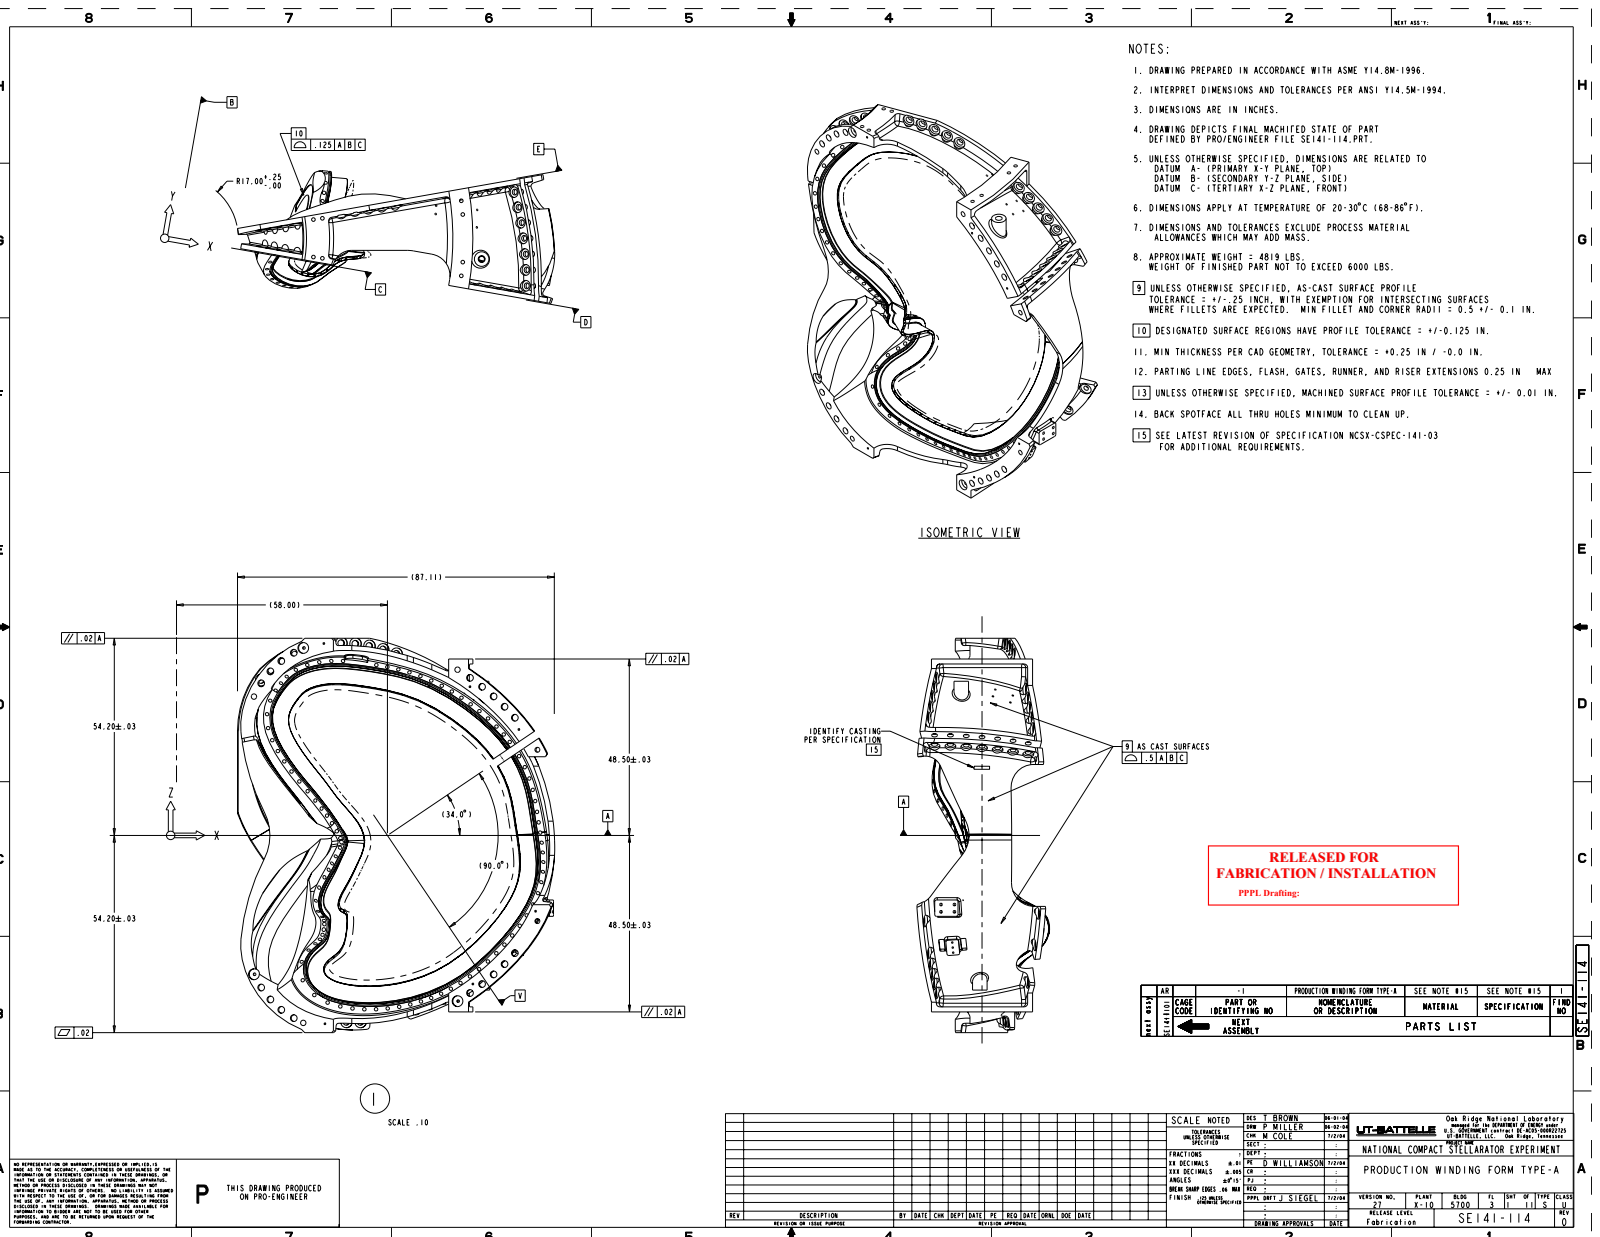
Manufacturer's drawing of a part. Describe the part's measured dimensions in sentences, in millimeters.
The part is named "SE141-114". Its 3-D file was written by "PRO/ENGINEER BY PARAMETRIC TECHNOLOGY CORPORATION, 2003490 (CONFIG_CONTROL_DESIGN)". It is 1 solid with 206 faces: 28 planar, 17 cylindrical and 161 other. Overall it measures 2753.4 by 2348 by 1114.7 millimeters. Its volume is 337 500 000 cubic millimeters and its surface area 16 410 000 square millimeters. Partial cylindrical surfaces (rounded edges, fillets, slot ends): 2 of radius 42.6, 2 of radius 1524, 1 of radius 355.6, 1 of radius 431.8, 1 of radius 667.8, 1 of radius 889, 1 of radius 1069.3, 1 of radius 1930.4. The main face-to-face distances are 144.8, 2608.6, 179.7, 2573.7, 34.9, 2428.9, 25.4, 2463.8, 2753.4, 2394.
